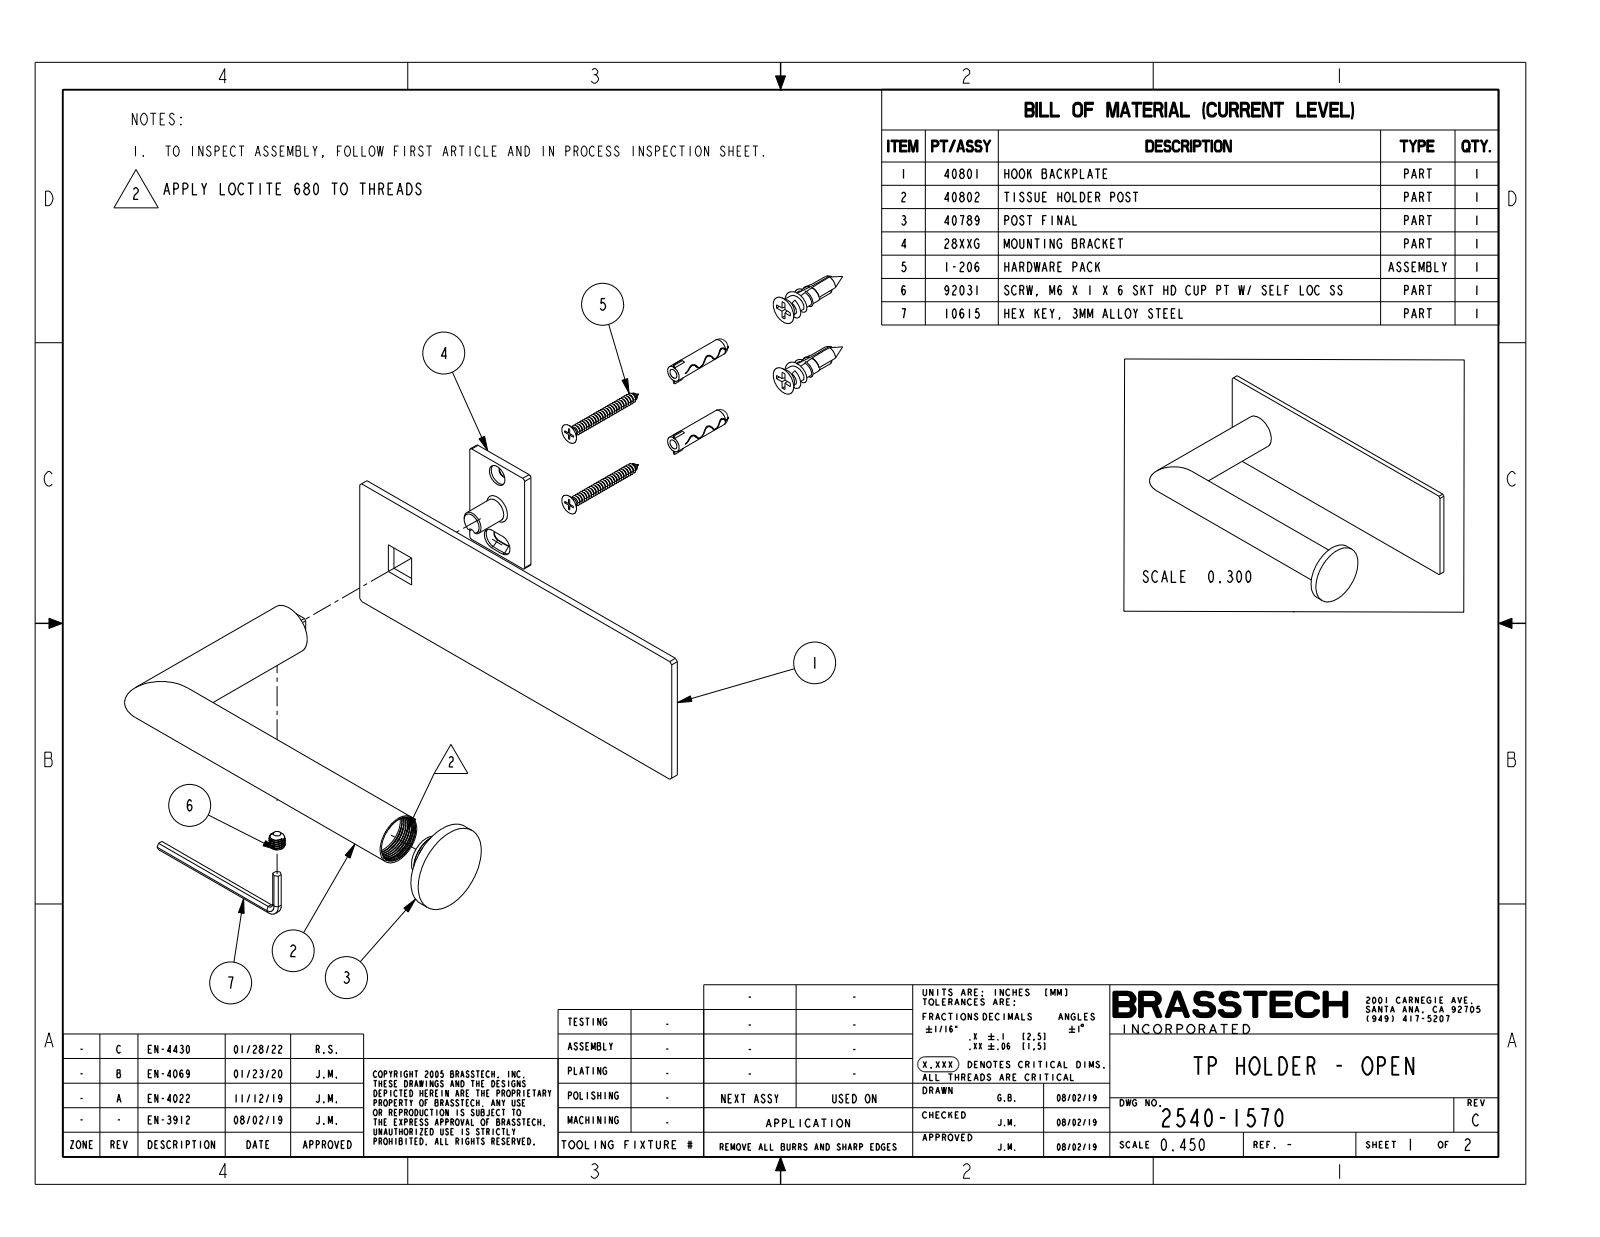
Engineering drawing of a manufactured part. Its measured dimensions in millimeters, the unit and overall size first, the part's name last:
Units: millimetres
Overall size (bounding box): 170.9 × 93.9 × 55.9
Round holes (diameter × count): ⌀5.1 ×1
Round bosses / shafts (diameter × count): ⌀20 ×2, ⌀34.5 ×1, ⌀12.7 ×1, ⌀11.5 ×1
Partial cylindrical surfaces — rounded edges, fillets, slot ends (radius × count): R1 ×4
Main face-to-face distances: 3, 3.5, 6.6, 4, 55.9, 6.5, 49.4, 152.1, 156.1, 170.9
Volume: 100 500 mm³ · Surface area: 35 410 mm²
Bodies: 1 solid, 44 faces (20 planar, 16 cylindrical, 8 other)
Part name (STEP PRODUCT): 2806R
STEP written by: CREO PARAMETRIC BY PTC INC, 2018400 (CONFIG_CONTROL_DESIGN)
